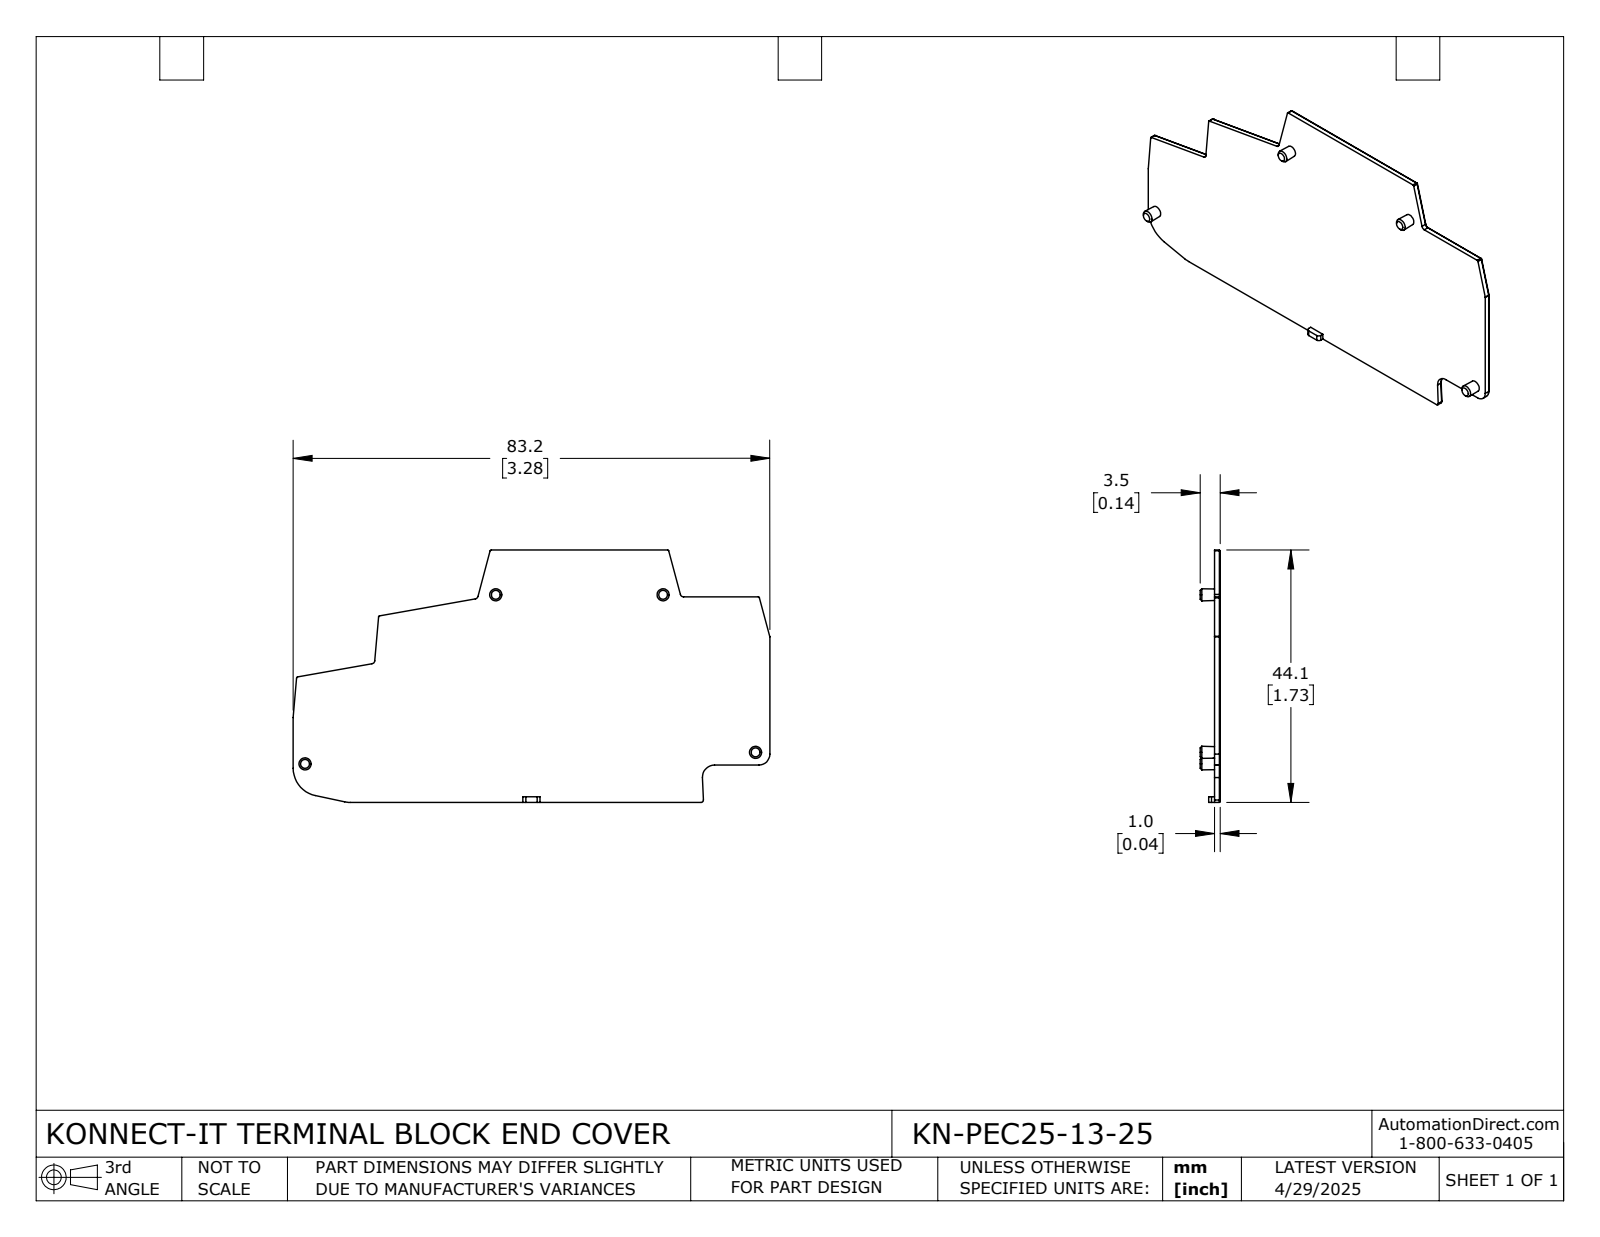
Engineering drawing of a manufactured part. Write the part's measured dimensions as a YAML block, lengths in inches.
part_name: "KN-PEC25-13-25"
step_written_by: "SolidWorks 2024 (CONFIG_CONTROL_DESIGN)"
units: inches
bodies: {solids: 1, faces: 92, planar: 41, cylindrical: 35, other: 16}
overall_size: [3.277, 1.735, 0.138]
volume: 0.181
surface_area: 9.593
partial_cylinders:
  - {radius: 0.004, count: 5}
  - {radius: 0.008, count: 5}
  - {radius: 0.024, count: 3}
  - {radius: 0.028, count: 3}
  - {radius: 0.012, count: 2}
  - {radius: 0.016, count: 2}
  - {radius: 0.02, count: 2}
  - {radius: 0.189, count: 2}
face_to_face_distances: [0.039, 1.735, 0.033, 1.731, 0.316, 0.322, 1.408, 1.412, 0.257, 0.098]
